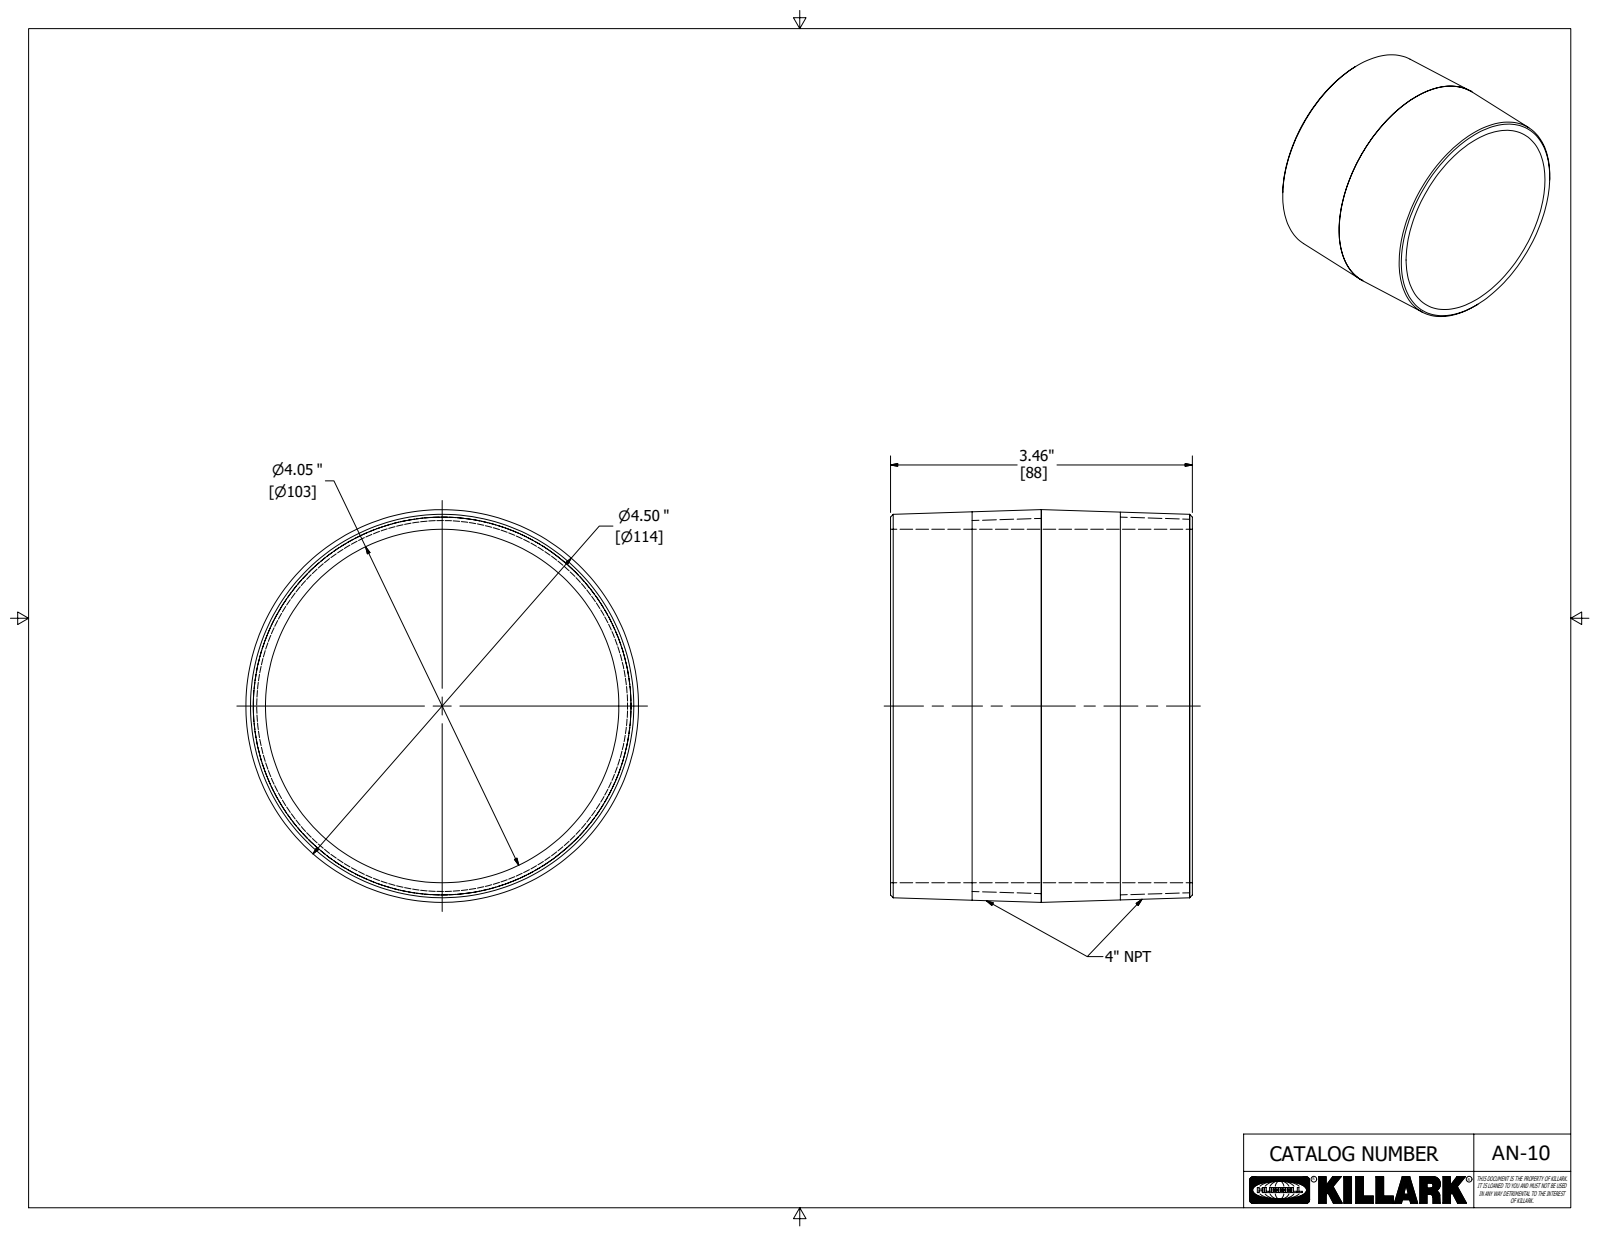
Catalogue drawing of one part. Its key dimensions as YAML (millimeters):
part_name: "14077-10"
step_written_by: "Autodesk Inventor 2020 (AUTOMOTIVE_DESIGN)"
units: millimeters
bodies: {solids: 1, faces: 8, planar: 2, cylindrical: 2, other: 4}
overall_size: [114.3, 114.3, 87.9]
volume: 149600
surface_area: 62210
round_holes:
  - {diameter: 102.9, count: 1}
round_bosses_or_shafts:
  - {diameter: 114.3, count: 1}
face_to_face_distances: [87.9]
